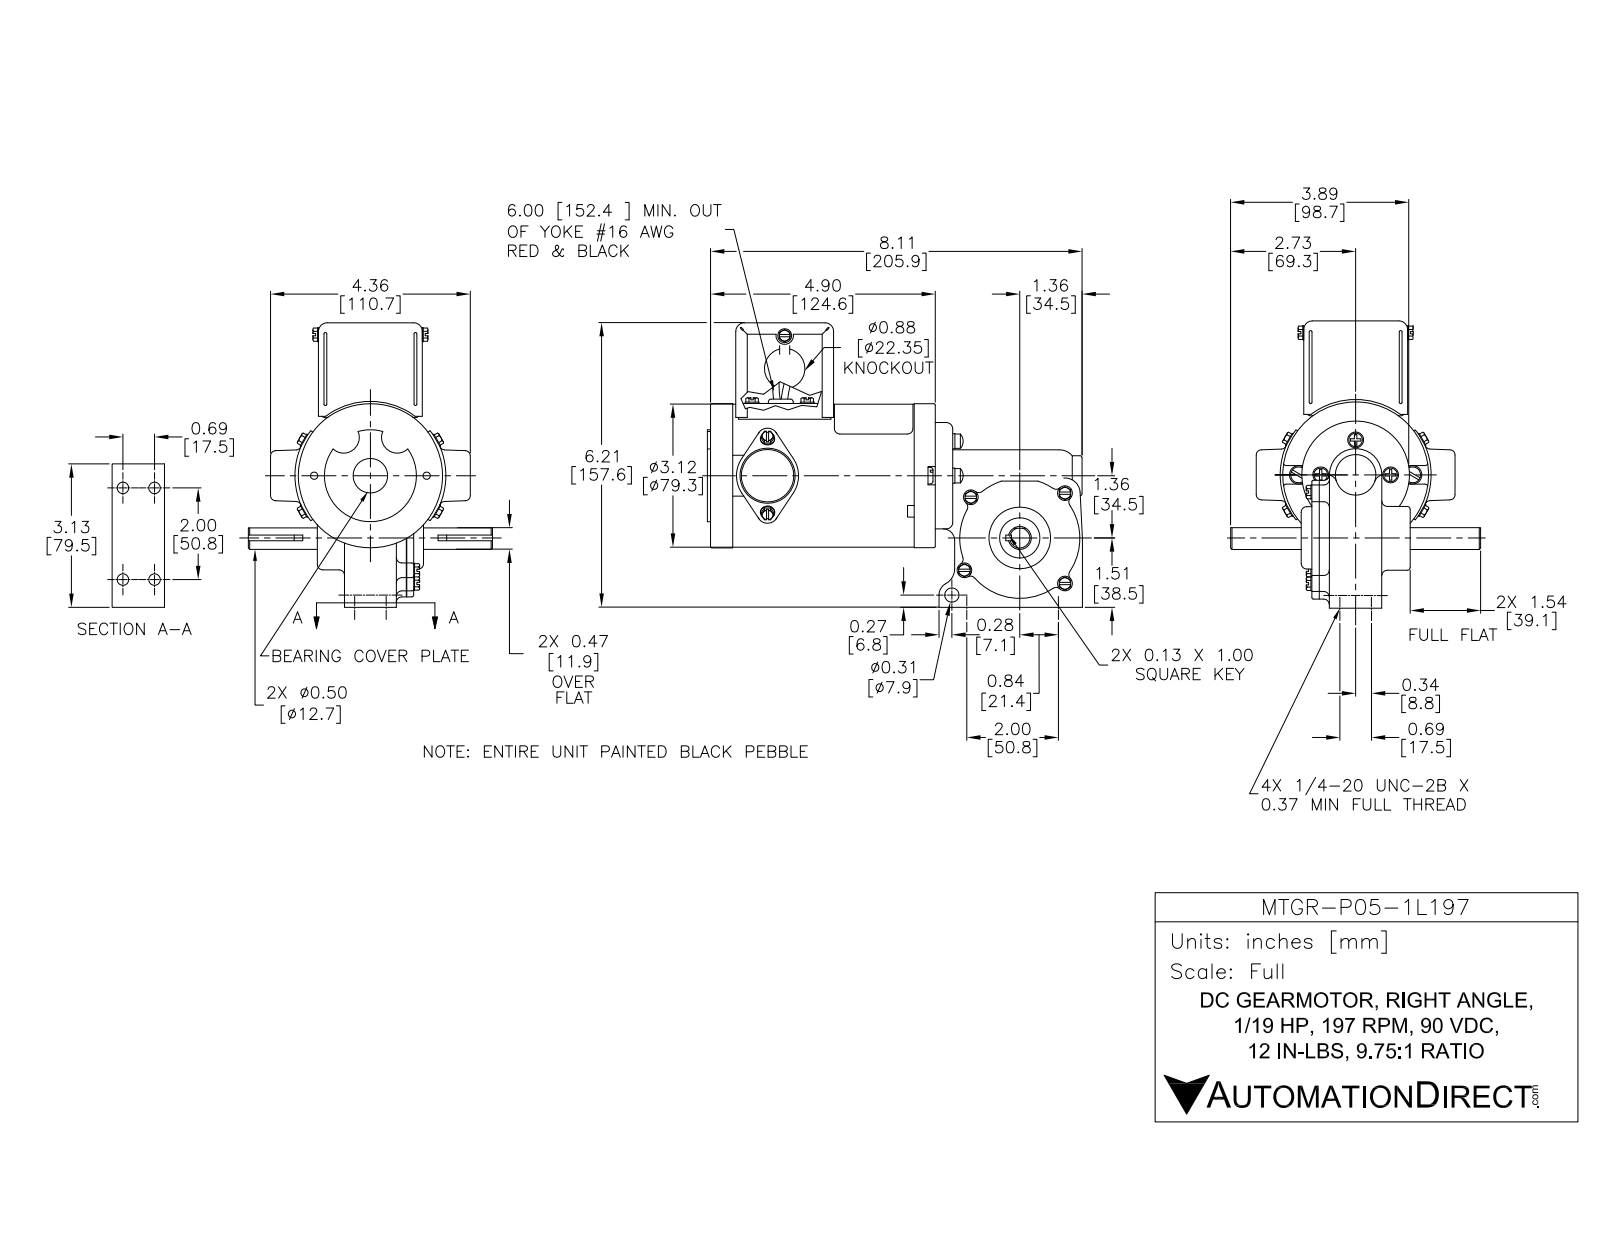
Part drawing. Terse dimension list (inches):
name: P05-1L197
written by: SolidWorks 2013 (AUTOMOTIVE_DESIGN)
unit: in
bodies: 40 solids, 712 faces (436 planar, 210 cylindrical, 66 other)
size: 8.179 × 6.274 × 5.453
volume: 27.37 in³; area: 297.1 in²
holes: 5× ⌀0.25, 2× ⌀0.094, 2× ⌀0.198, 1× ⌀0.3, 1× ⌀0.301, 1× ⌀0.375, 1× ⌀0.5, 1× ⌀0.86, 1× ⌀1.225, 1× ⌀3, 1× ⌀3.125
bosses: 4× ⌀0.321, 4× ⌀0.3, 3× ⌀0.346, 3× ⌀0.295, 2× ⌀0.125, 2× ⌀0.1, 1× ⌀3.156, 1× ⌀3.14
rounds: 10× R0.1, 4× R0.191, 4× R0.234, 2× R0.15, 2× R0.159, 2× R0.341, 1× R0.25, 1× R0.34
face distances: 0.031, 0.25, 0.063, 4.65, 2.135, 0.307, 2.047, 1.67, 1.608, 0.245
hole spacings: 0.343, 0.456, 0.686, 1.23, 2, 2.029, 2.114, 2.326
